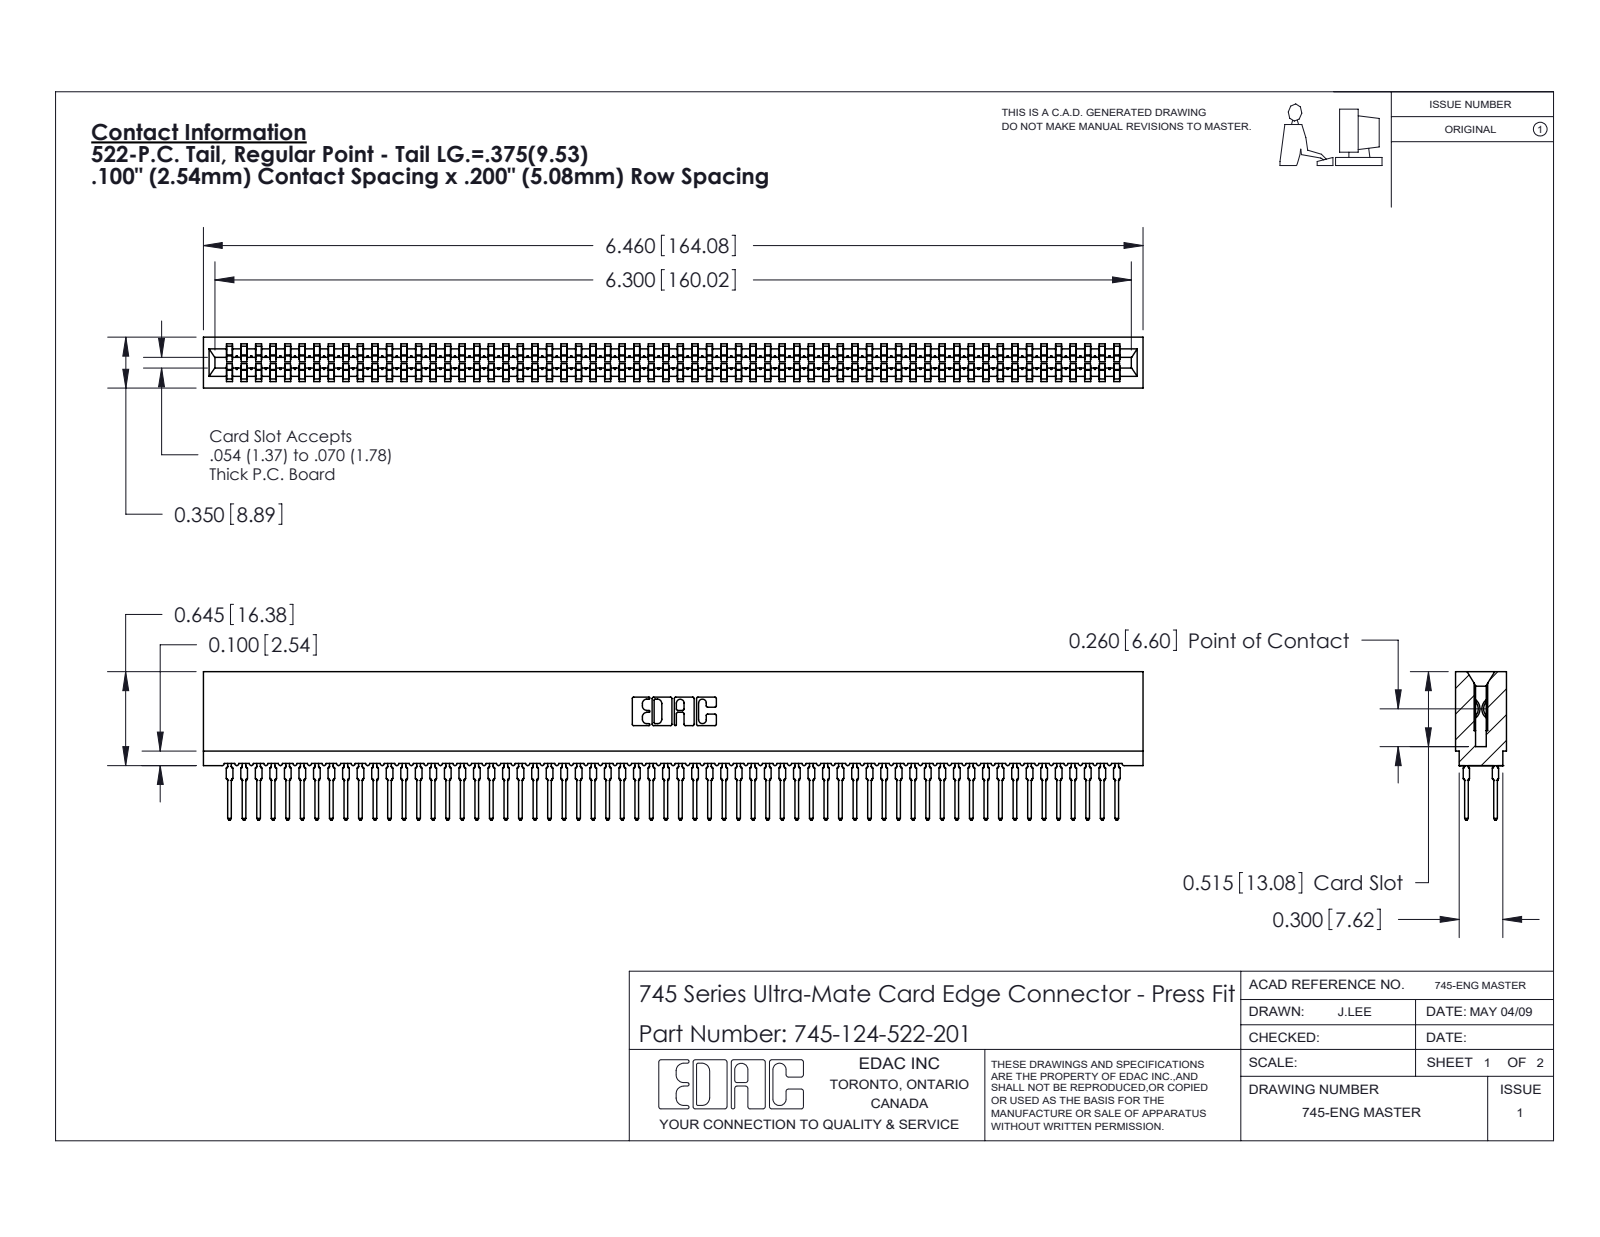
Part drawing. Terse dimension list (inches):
name: 745-292-001_522; 745 Part_Insulator Option - 01; 745-124-522-201
written by: SolidWorks 2020 (CONFIG_CONTROL_DESIGN)
unit: in
bodies: 125 solids, 11193 faces (5759 planar, 2210 cylindrical, 3224 other)
size: 6.46 × 1.021 × 0.35
volume: 0.902 in³; area: 47.98 in²
rounds: 248× R0.021, 124× R0.015, 22× R0.01, 8× R0.005, 8× R0.011, 6× R0.007, 6× R0.031, 3× R0.026
face distances: 0.35, 0.063, 0.287, 0.045, 0.305, 0.018, 0.243, 0.138, 0.212, 0.093
